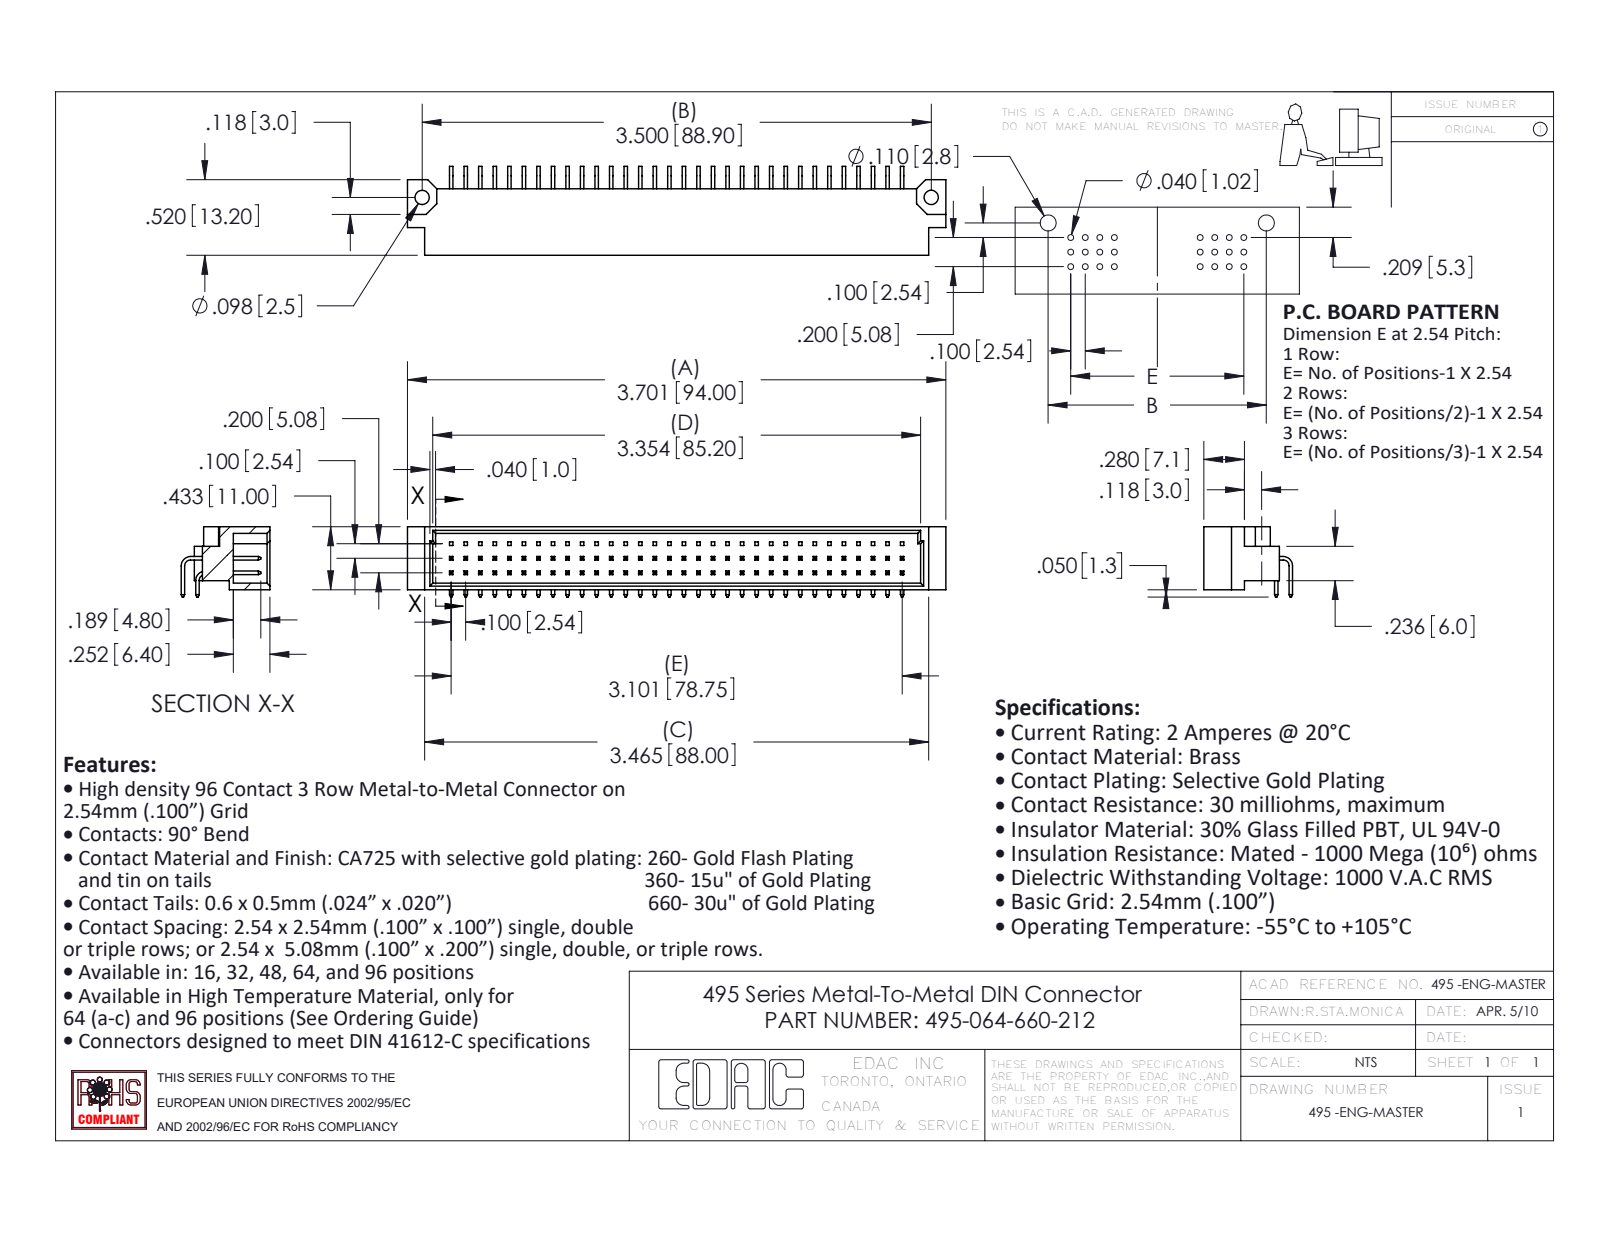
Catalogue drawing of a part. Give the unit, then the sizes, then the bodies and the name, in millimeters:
Units: millimetres
Overall size (bounding box): 94 × 15.51 × 12.27
Round holes (diameter × count): ⌀2.49 ×2
Partial cylindrical surfaces — rounded edges, fillets, slot ends (radius × count): R1.02 ×2, R1.65 ×2
Main face-to-face distances: 2.54, 5.2, 1.14, 9.86, 0.61, 11, 8.72, 1.6, 9.4, 3.15
Hole centre spacings: 88.9
Volume: 6 330 mm³ · Surface area: 9 514 mm²
Bodies: 65 solids, 1585 faces (1453 planar, 132 cylindrical, 0 other)
Part name (STEP PRODUCT): 495-064-660-212; 495-290-3; 495 Part_96; 495-290-2
STEP written by: SolidWorks 2020 (AUTOMOTIVE_DESIGN)
